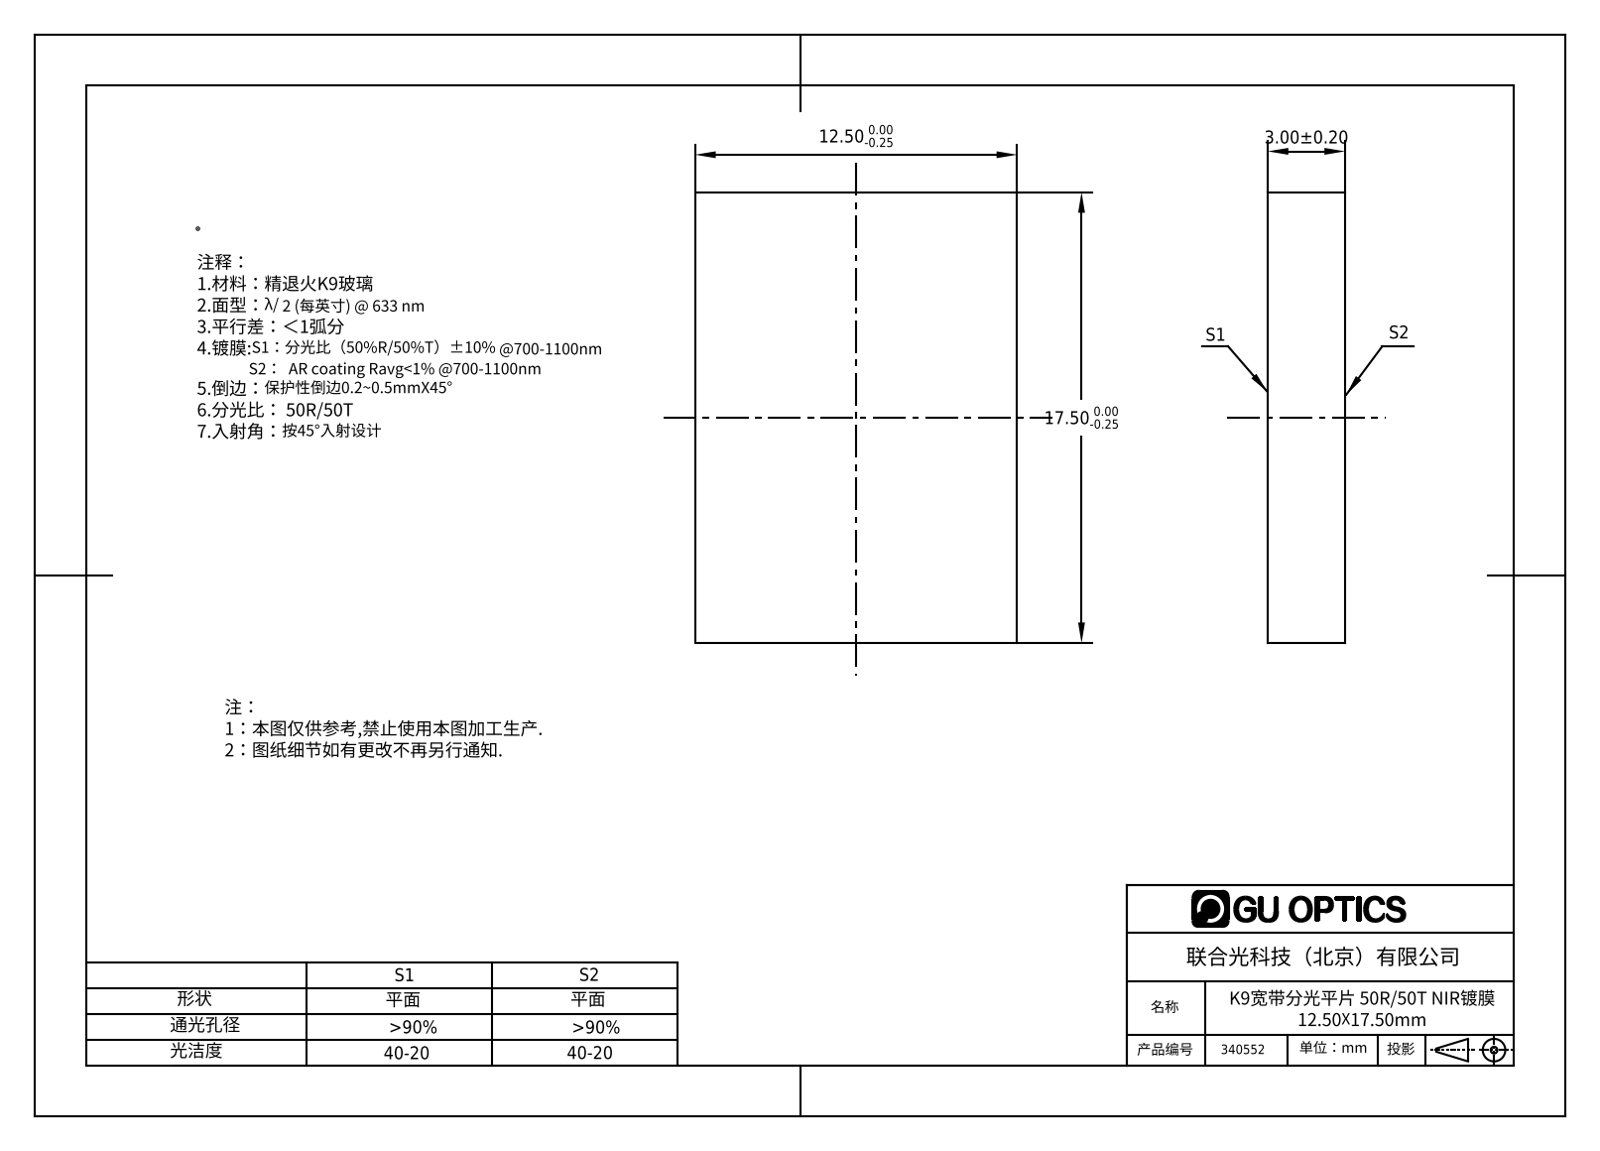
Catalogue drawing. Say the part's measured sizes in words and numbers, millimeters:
The part is named "340507". Its 3-D file was written by "SolidWorks 2016 (CONFIG_CONTROL_DESIGN)". It is 1 solid with 6 faces: 6 planar, 0 cylindrical and 0 other. Overall it measures 17.5 by 12.5 by 3 millimeters. Its volume is 656 cubic millimeters and its surface area 618 square millimeters. The main face-to-face distances are 3, 12.5, 17.5.
